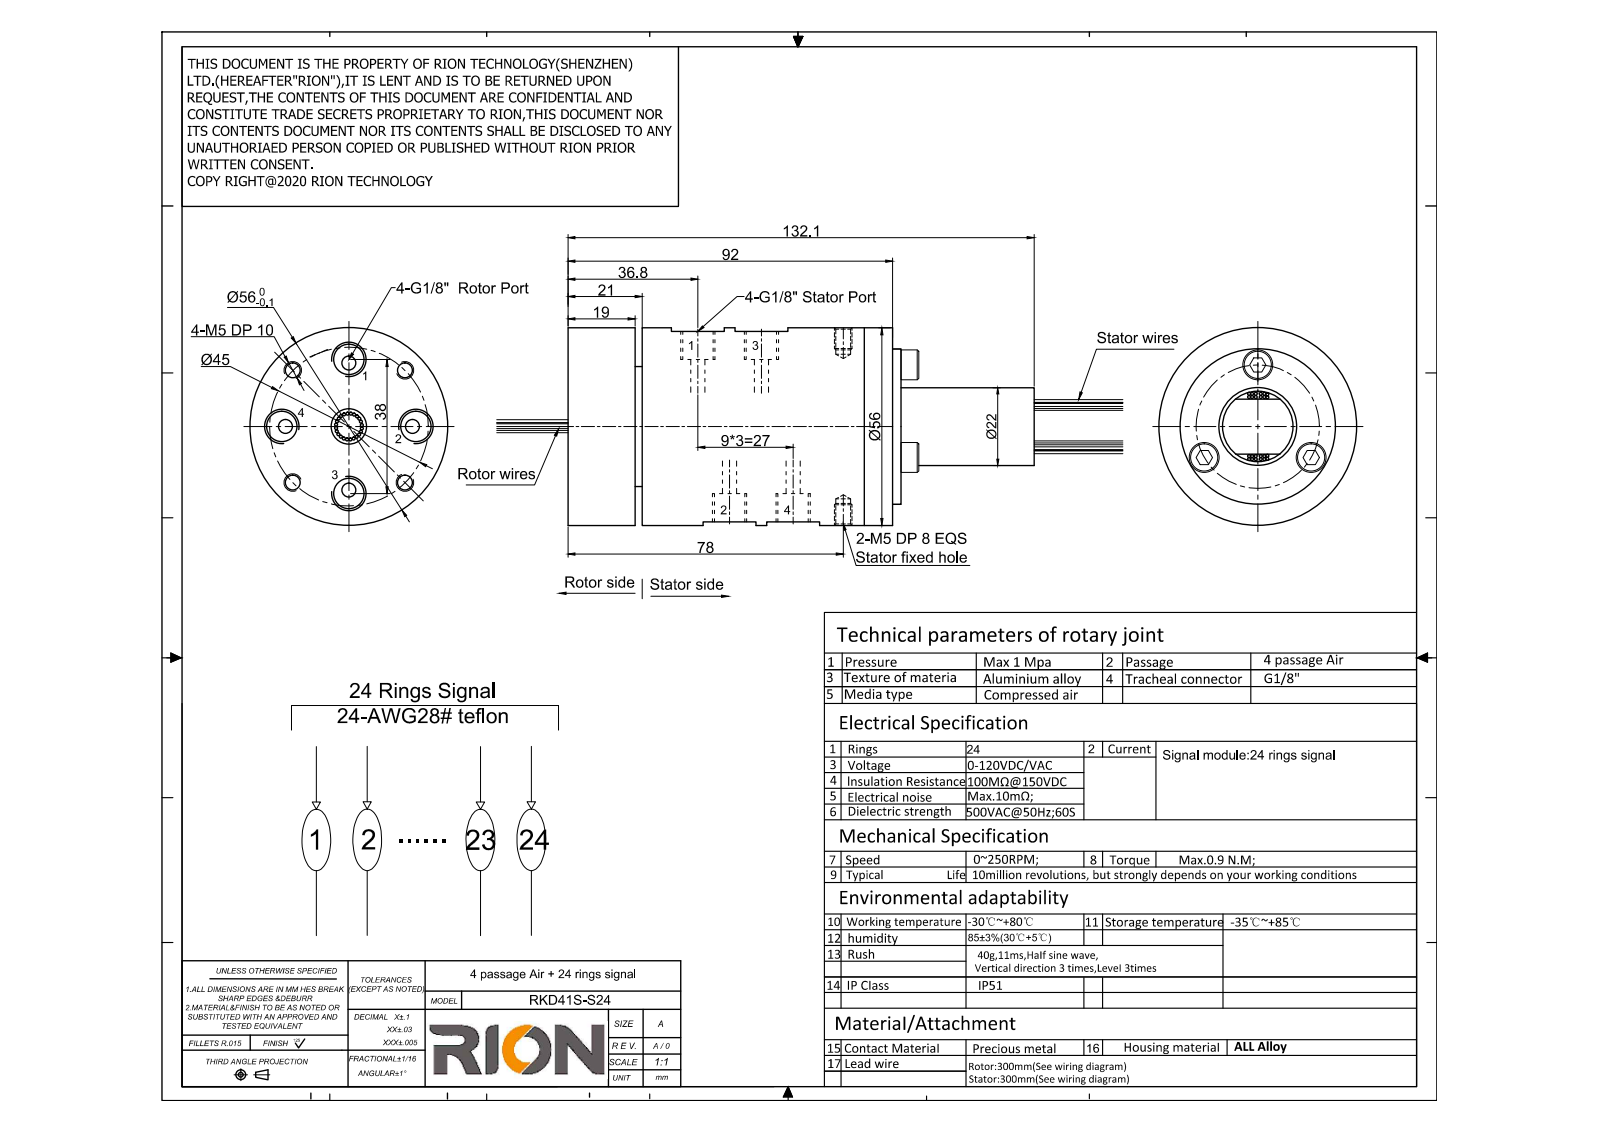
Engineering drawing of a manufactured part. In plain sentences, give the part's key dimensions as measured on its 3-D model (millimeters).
The part is named "RKD41S-S24". Its 3-D file was written by "SolidWorks 2014 (CONFIG_CONTROL_DESIGN)". It is 1 solid with 305 faces: 106 planar, 165 cylindrical and 34 other. Overall it measures 172 by 56 by 56 millimeters. Its volume is 235 468 cubic millimeters and its surface area 33 904 square millimeters. Round holes: 9 of diameter 4, 8 of diameter 8.8, 5 of diameter 4.2, 1 of diameter 9.5, 1 of diameter 20. Round bosses or shafts: 48 of diameter 0.8, 3 of diameter 8.5, 1 of diameter 56, 1 of diameter 44, 1 of diameter 34, 1 of diameter 22, 1 of diameter 19.9. The main face-to-face distances are 19, 21, 2, 94.4, 75.4, 73.4, 92, 73, 71, 2.4. The hole center spacings are 16.05, 16.21, 26.17, 37.46, 38.36, 18, 1, 19.
